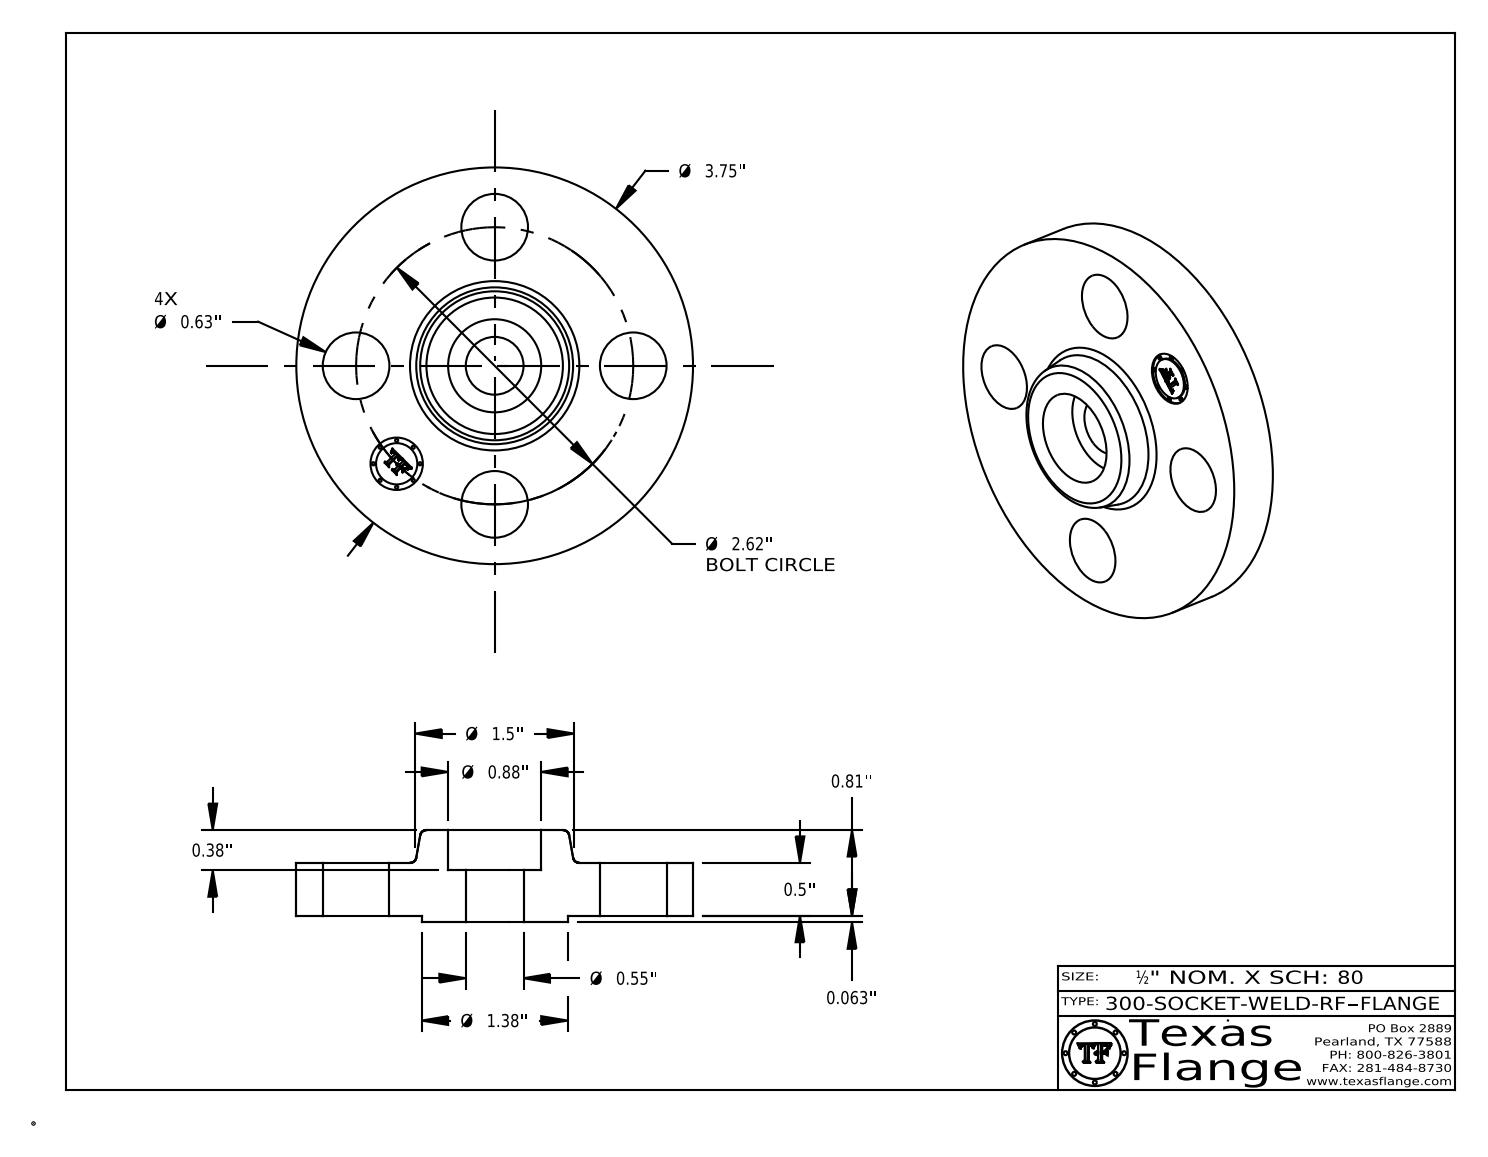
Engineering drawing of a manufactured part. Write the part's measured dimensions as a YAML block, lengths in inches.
part_name: "300-SOCKET-WELD-RF"
step_written_by: "CATIA V5 STEP AP214 (AUTOMOTIVE_DESIGN)"
units: inches
bodies: {solids: 1, faces: 412, planar: 370, cylindrical: 36, other: 6}
overall_size: [3.75, 3.75, 0.873]
volume: 5.154
surface_area: 32.26
round_holes:
  - {diameter: 0.63, count: 4}
  - {diameter: 0.495, count: 1}
  - {diameter: 0.546, count: 1}
  - {diameter: 0.88, count: 1}
round_bosses_or_shafts:
  - {diameter: 0.03, count: 8}
  - {diameter: 3.75, count: 1}
  - {diameter: 1.38, count: 1}
  - {diameter: 0.39, count: 1}
face_to_face_distances: [0.5, 0.063, 0.563, 0.872, 0.81, 0.31, 0.07, 0.493, 0.43, 0.38]
hole_center_spacings: [1.31, 1.852, 1.003, 2.42, 2.62, 1.31]
